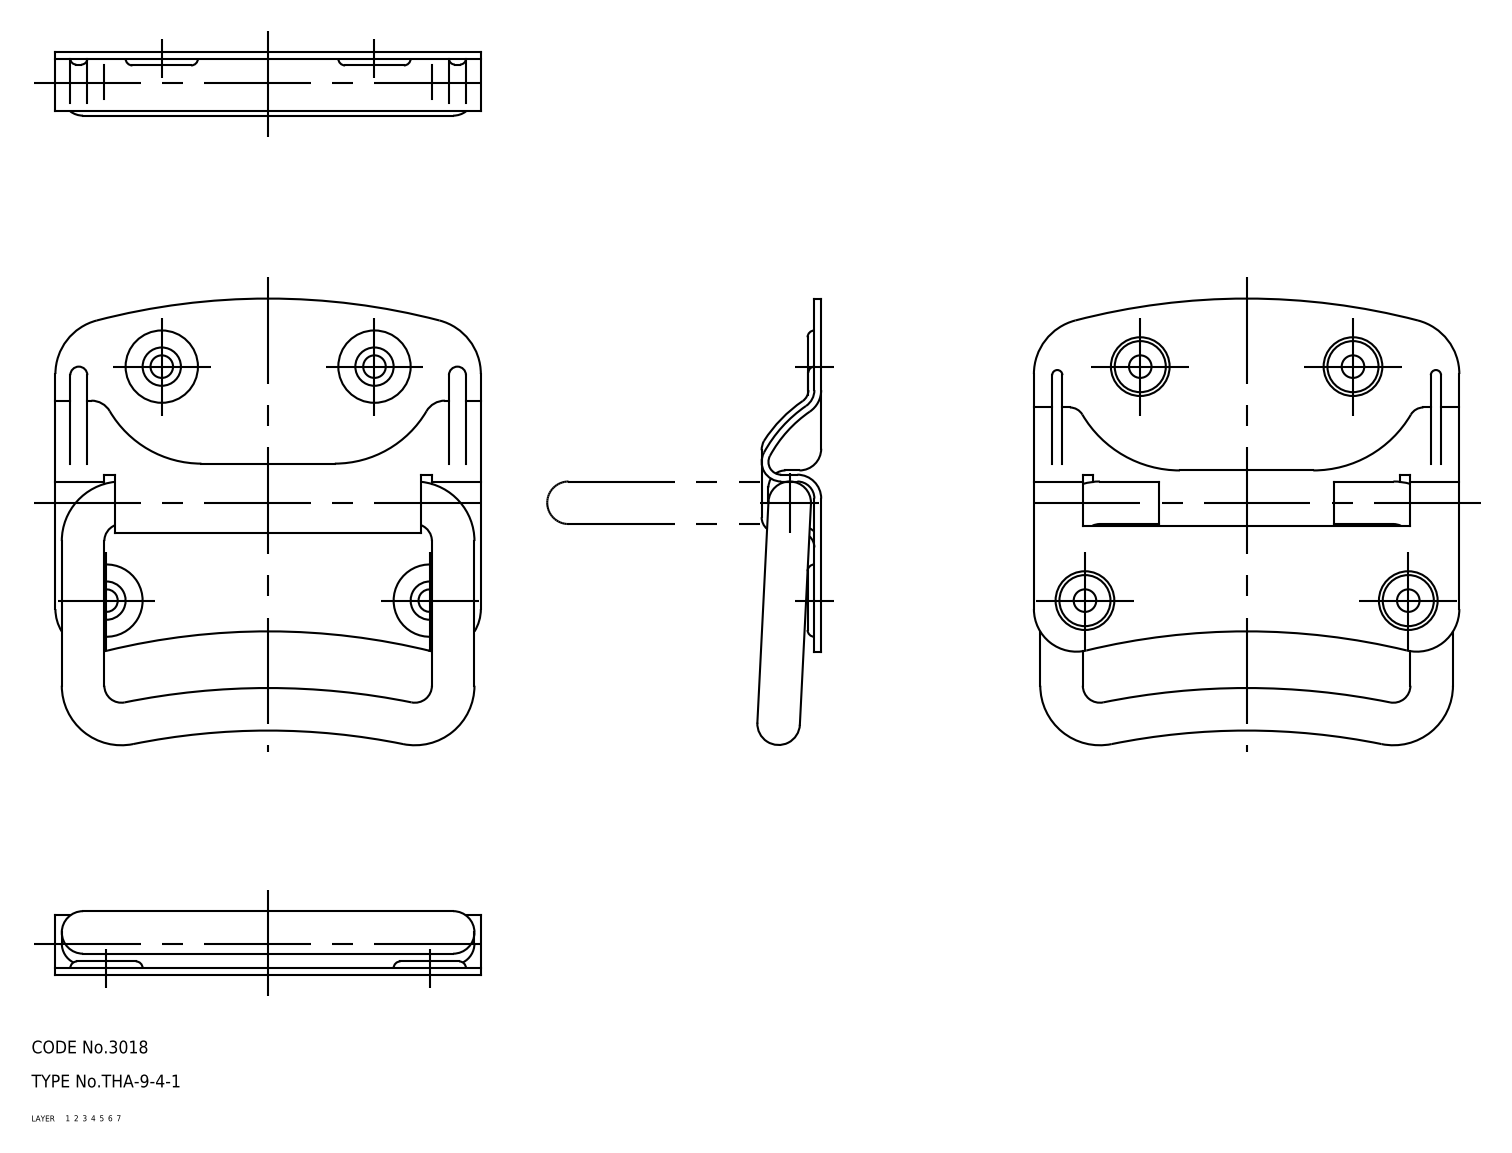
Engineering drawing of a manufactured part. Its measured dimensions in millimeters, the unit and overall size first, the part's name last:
Units: millimetres
Overall size (bounding box): 105 × 100 × 15
Volume: 32 848 mm³ · Surface area: 27 169 mm²
Bodies: 2 solids, 268 faces (0 planar, 0 cylindrical, 268 other)
Part name (STEP PRODUCT): grip; base; THA_9_4_1_4042_36
STEP written by: CADfix (AUTOMOTIVE_DESIGN)
